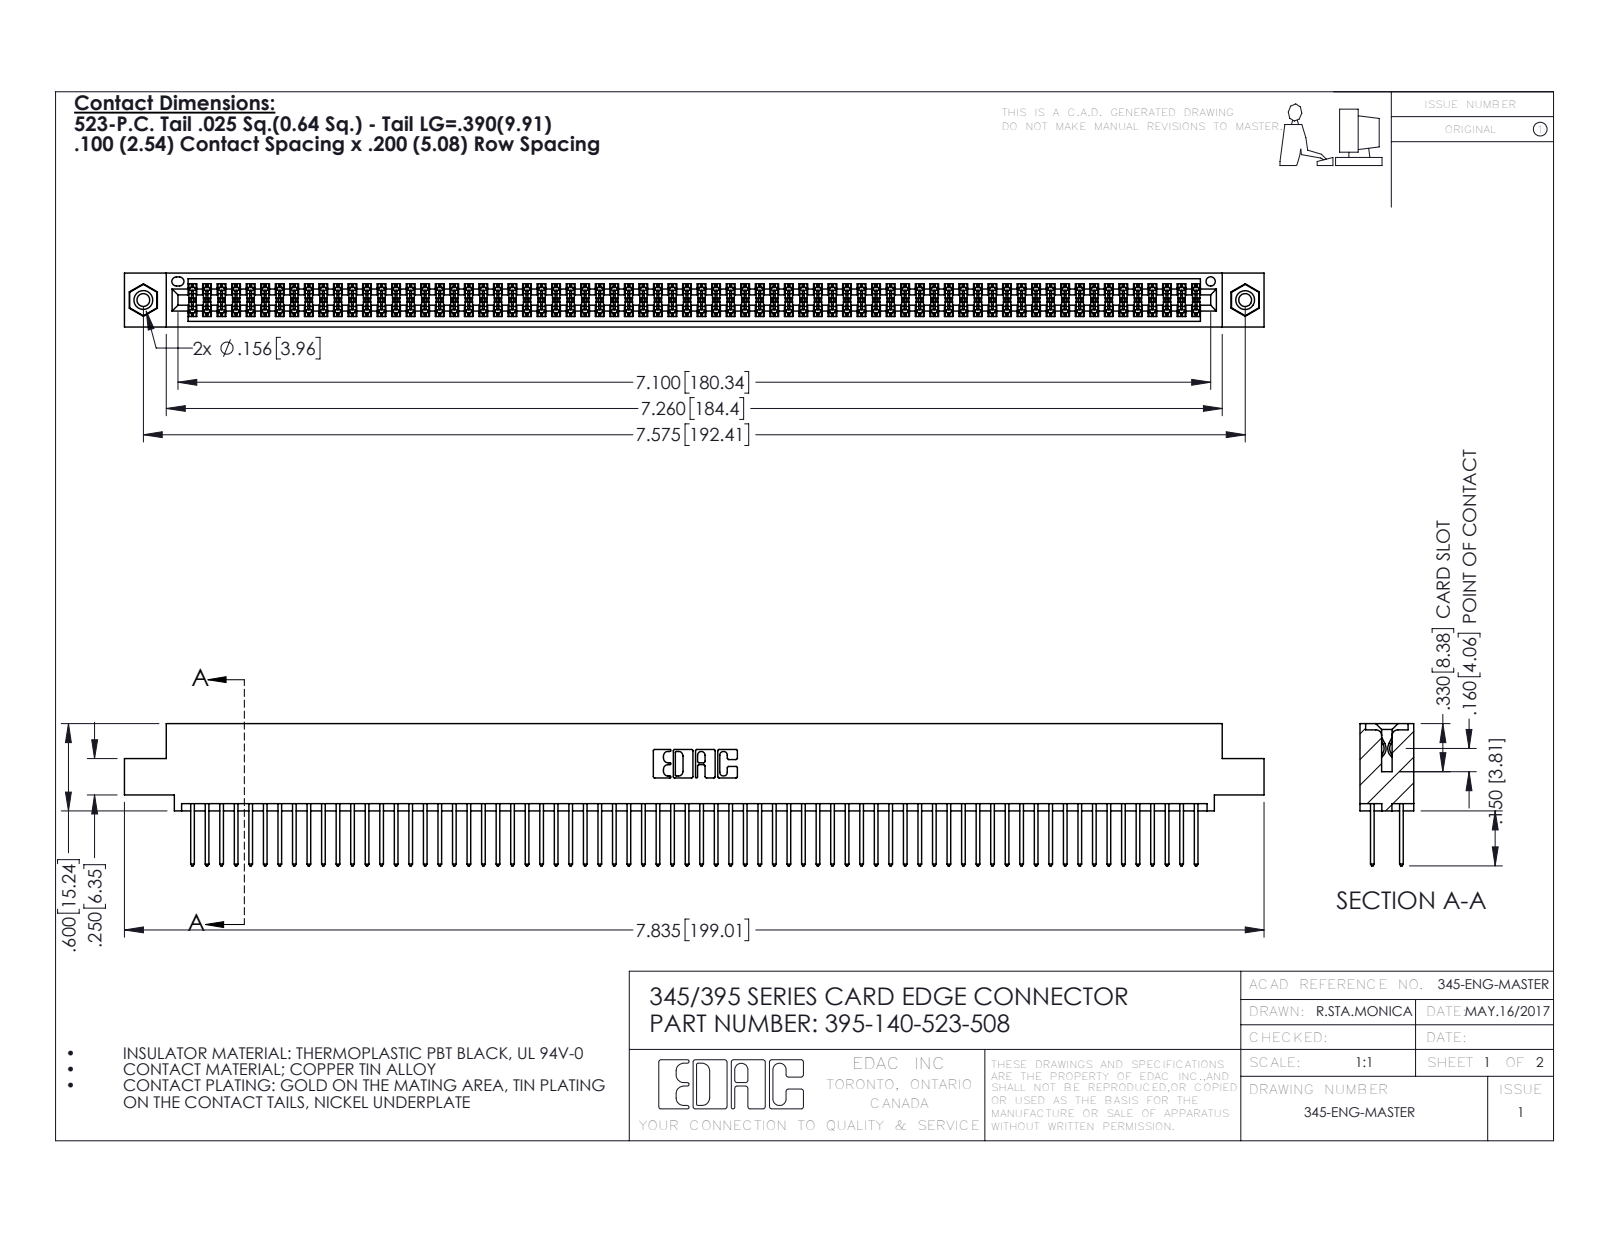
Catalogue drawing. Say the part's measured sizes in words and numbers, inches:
The part is named "345-250-001_345-250-003-102; 395-140-523-508; 345 Part_0.110 Offset - 0.156 Dia-TI; 345-292-001_345-293-123". Its 3-D file was written by "SolidWorks 2016 (CONFIG_CONTROL_DESIGN)". It is 143 solids with 7190 faces: 4736 planar, 2438 cylindrical and 16 other. Overall it measures 7.835 by 0.977 by 0.37 inches. Its volume is 1.208 cubic inches and its surface area 48.36 square inches. Round holes: 2 of diameter 0.089, 2 of diameter 0.125, 2 of diameter 0.156, 1 of diameter 0.064. Round bosses or shafts: 2 of diameter 0.155. Partial cylindrical surfaces (rounded edges, fillets, slot ends): 210 of radius 0.006, 140 of radius 0.01, 22 of radius 0.01, 6 of radius 0.007, 6 of radius 0.031, 3 of radius 0.026, 2 of radius 0.014, 2 of radius 0.019. The main face-to-face distances are 0.072, 0.298, 0.2, 0.098, 0.272, 0.025, 0.37, 0.225, 0.175, 0.149. The hole center spacings are 0.27, 7.339, 7.575.
